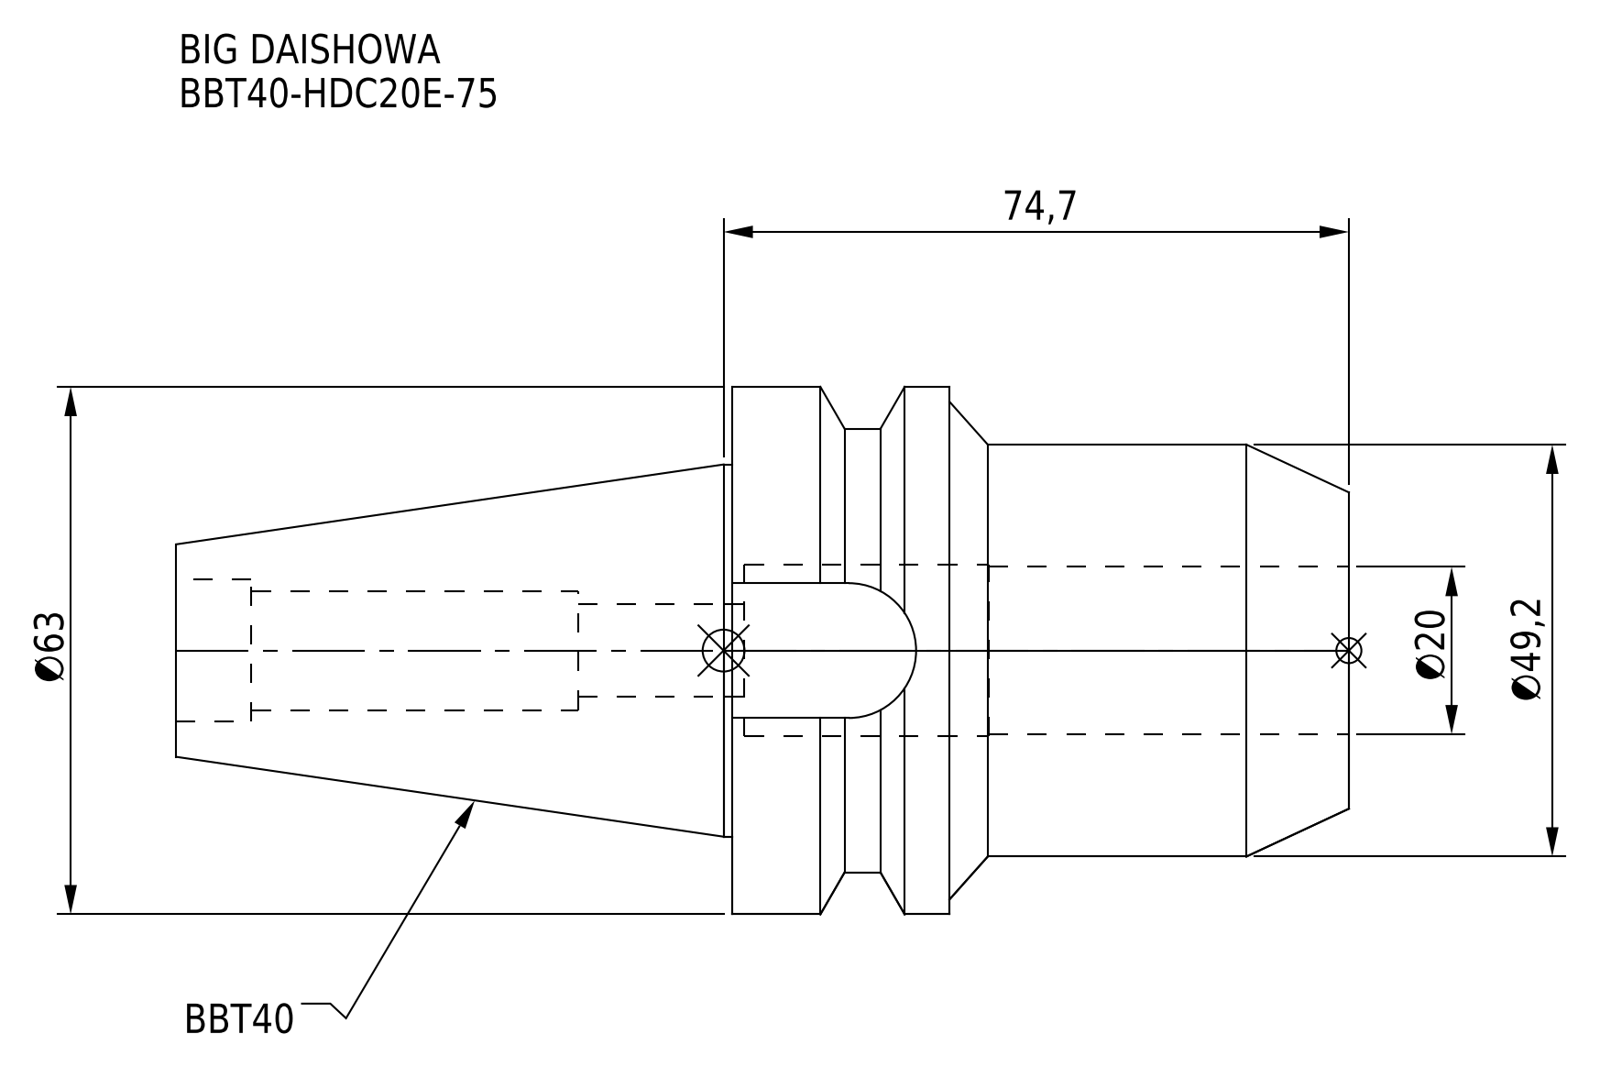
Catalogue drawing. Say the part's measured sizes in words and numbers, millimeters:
The part is named "BBT40-HDC20E-75". Its 3-D file was written by "CREO PARAMETRIC BY PTC INC, 2016380 (AUTOMOTIVE_DESIGN)". It is 1 solid with 48 faces: 14 planar, 24 cylindrical and 10 other. Overall it measures 140.1 by 63 by 63 millimeters. Its volume is 189 949 cubic millimeters and its surface area 32 282 square millimeters. Round holes: 1 of diameter 11, 1 of diameter 14.2, 1 of diameter 17, 1 of diameter 20, 1 of diameter 20.5. Round bosses or shafts: 1 of diameter 63, 1 of diameter 53, 1 of diameter 49.2, 1 of diameter 44.45. Partial cylindrical surfaces (rounded edges, fillets, slot ends): 1 of radius 8.05. The main face-to-face distances are 73.7, 47.7, 26, 45, 140.1, 92.4, 66.4, 72.2, 24.5, 1.5.
